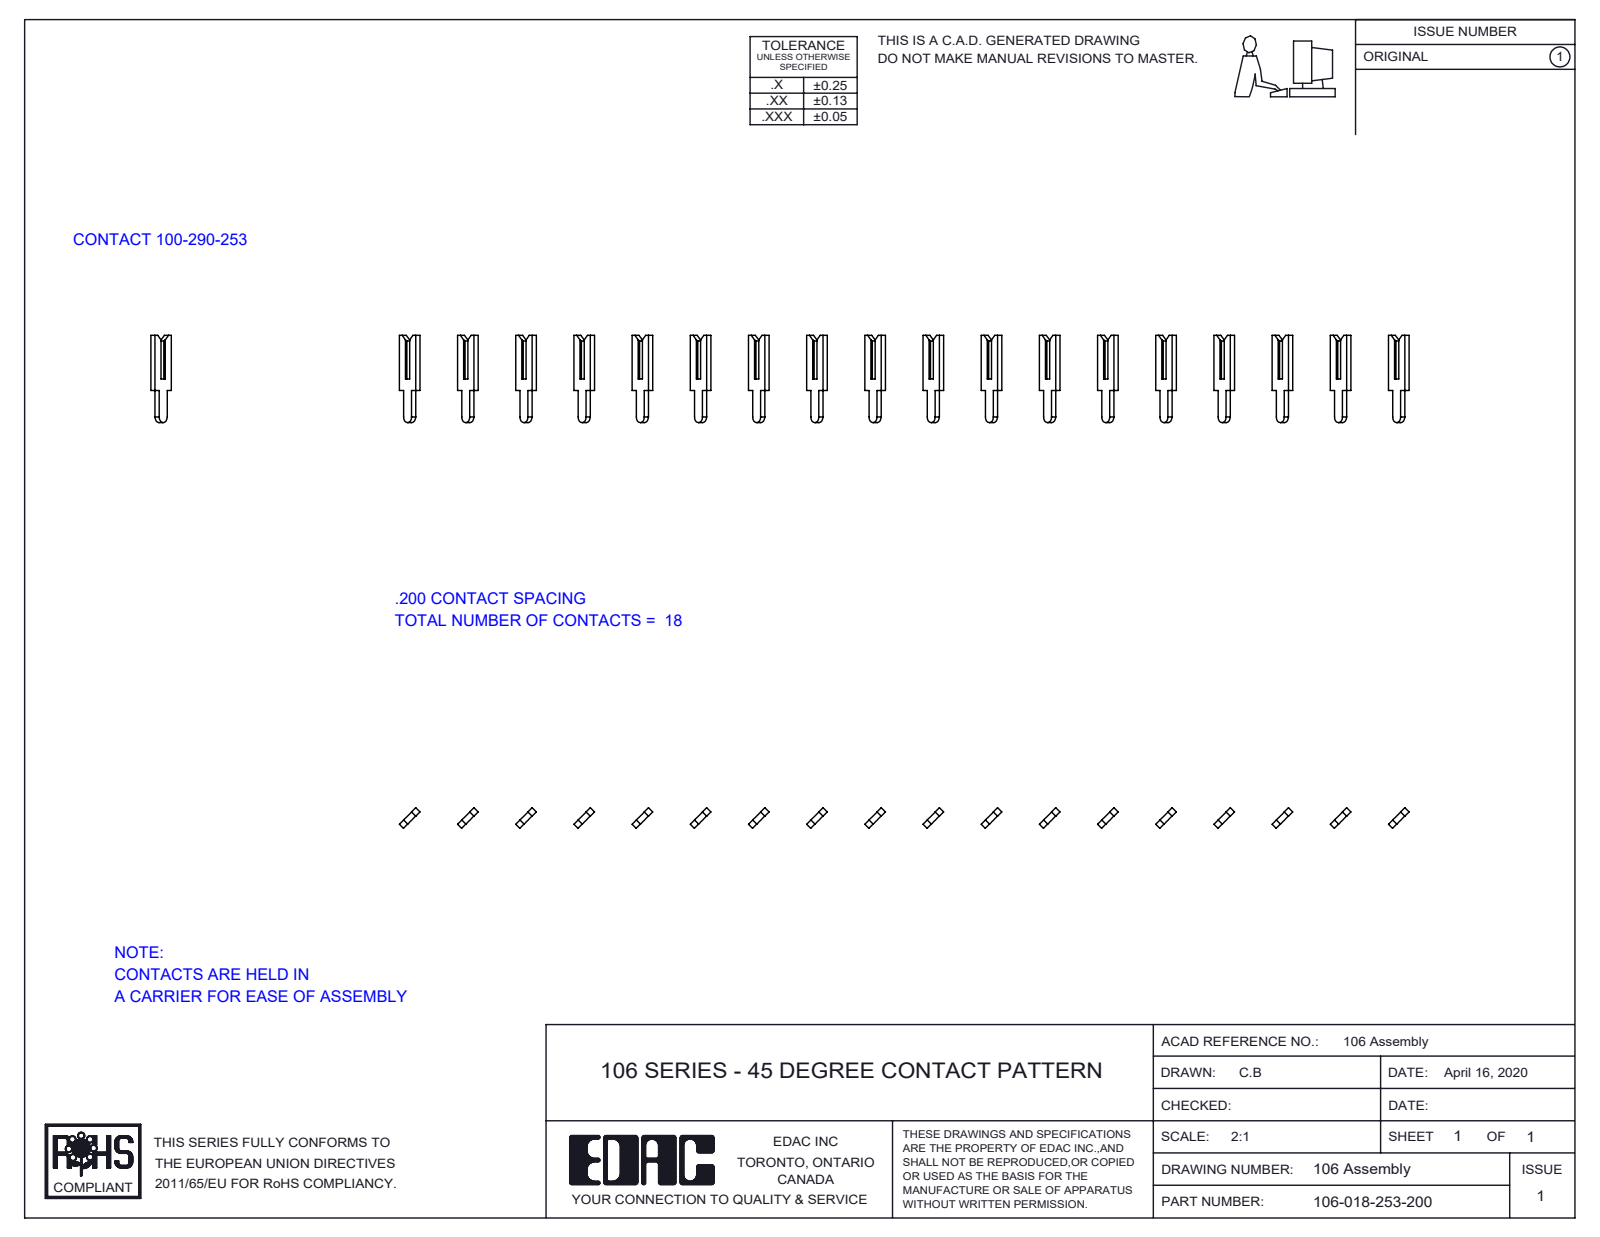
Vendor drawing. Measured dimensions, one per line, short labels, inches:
name: 100-290-001_100-290-253; 106-018-253-200
written by: SolidWorks 2016 (CONFIG_CONTROL_DESIGN)
unit: in
bodies: 18 solids, 360 faces (342 planar, 18 cylindrical, 0 other)
size: 3.471 × 0.3 × 0.071
volume: 0.006 in³; area: 0.96 in²
rounds: 18× R0.019
face distances: 0.141, 0.848, 0.283, 0.707, 0.99, 0.566, 0.424, 0.424, 1.131, 0.283
